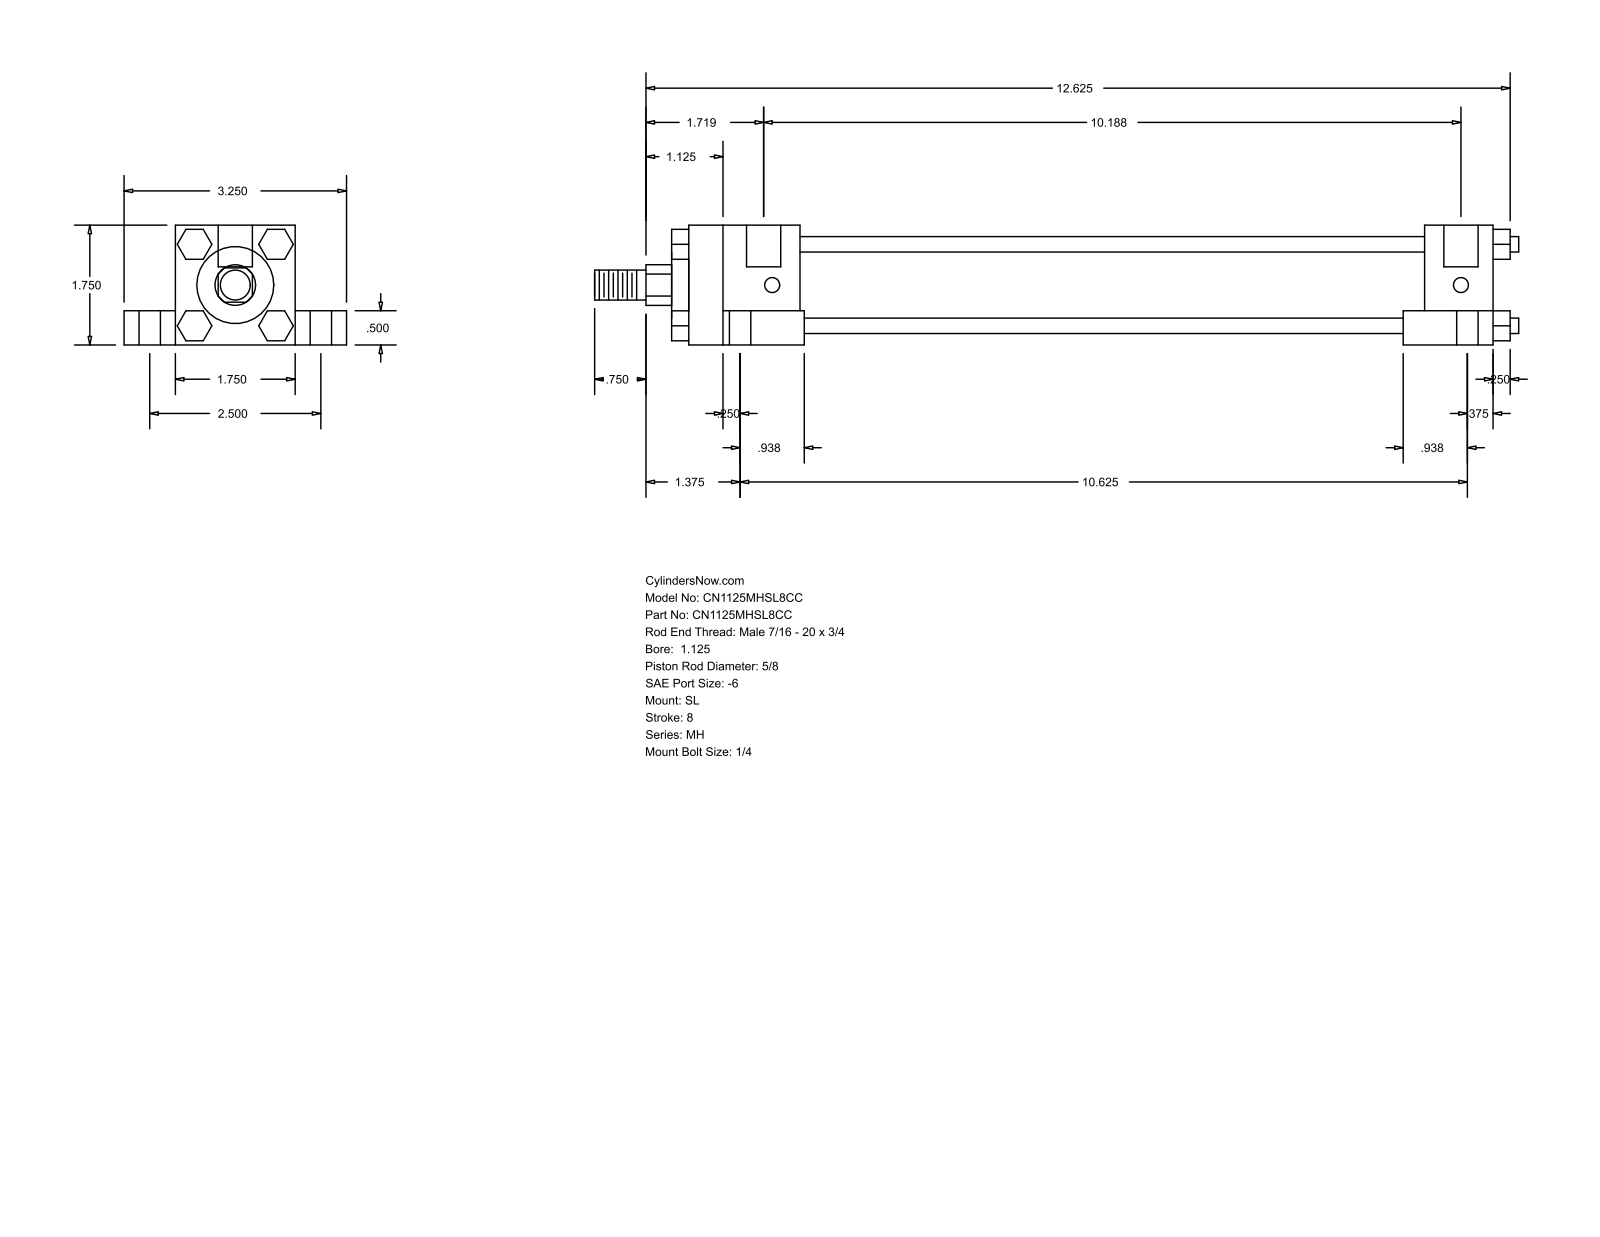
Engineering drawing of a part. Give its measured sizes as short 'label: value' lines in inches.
name: MH_SL__0112_0.625
written by: GSSL Pune (CONFIG_CONTROL_DESIGN)
unit: in
bodies: 0 solids, 150 faces (114 planar, 36 cylindrical, 0 other)
size: 13.5 × 3.25 × 1.75
holes: 4× ⌀0.219, 4× ⌀0.313, 4× ⌀0.563, 2× ⌀0.5
bosses: 4× ⌀0.225, 1× ⌀1.375, 1× ⌀1.125, 1× ⌀0.625, 1× ⌀0.437
rounds: 1× R0.297
face distances: 1.75, 0.75, 0.5, 1.25, 2.5, 0.437, 1.875, 9.125, 10.125, 1
hole spacings: 1.254, 1.269, 1.296, 2.5, 10.063, 10.233, 10.357, 10.481
